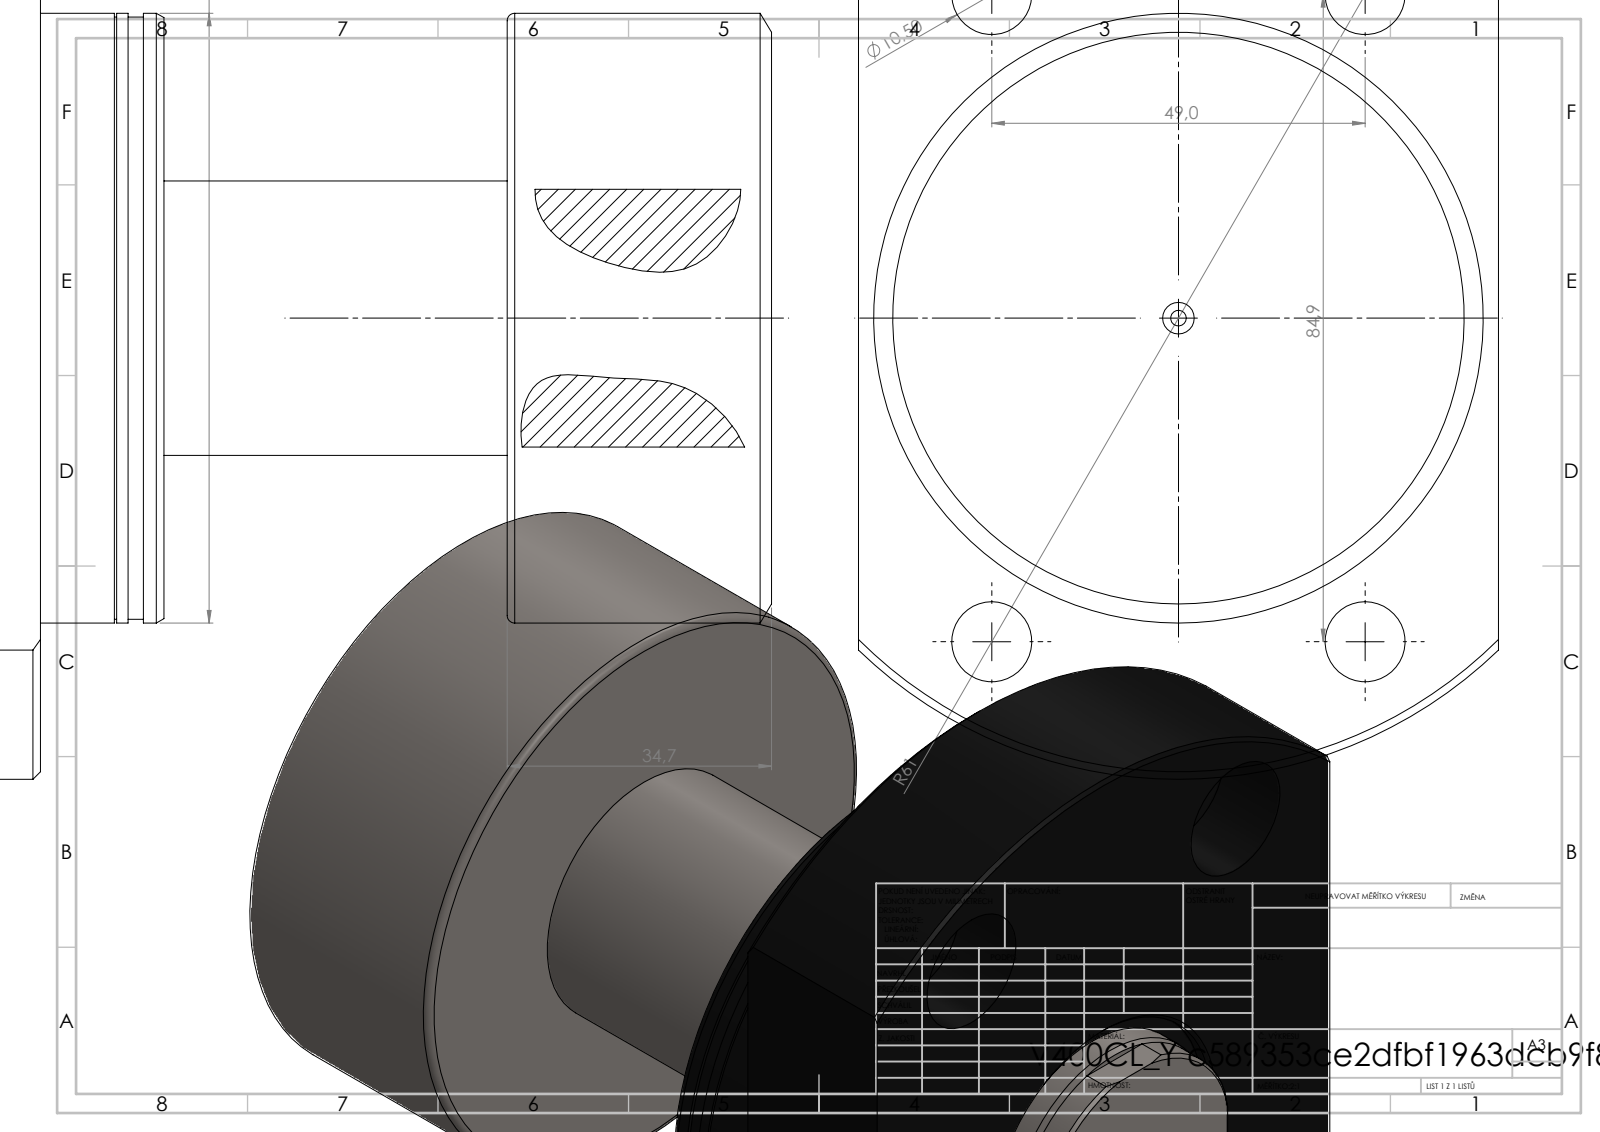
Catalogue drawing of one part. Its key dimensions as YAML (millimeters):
part_name: "V400CL_VC_X; V400CL_PC_Y"
step_written_by: "SolidWorks 2019 (CONFIG_CONTROL_DESIGN)"
units: millimeters
bodies: {solids: 2, faces: 103, planar: 26, cylindrical: 47, other: 30}
overall_size: [126, 121, 84]
volume: 514413
surface_area: 66243
round_holes:
  - {diameter: 10.5, count: 4}
  - {diameter: 16.5, count: 4}
  - {diameter: 2.05, count: 1}
  - {diameter: 5, count: 1}
  - {diameter: 6, count: 1}
  - {diameter: 36, count: 1}
  - {diameter: 40.5, count: 1}
round_bosses_or_shafts:
  - {diameter: 80, count: 1}
  - {diameter: 79, count: 1}
partial_cylinders:
  - {radius: 17.75, count: 1}
  - {radius: 60.5, count: 1}
face_to_face_distances: [119.95, 34.7, 85.25, 79.75, 45.05, 40.2, 95.95, 61.25, 16.2, 24]
hole_center_spacings: [49.01, 49, 84.9, 98.03]
